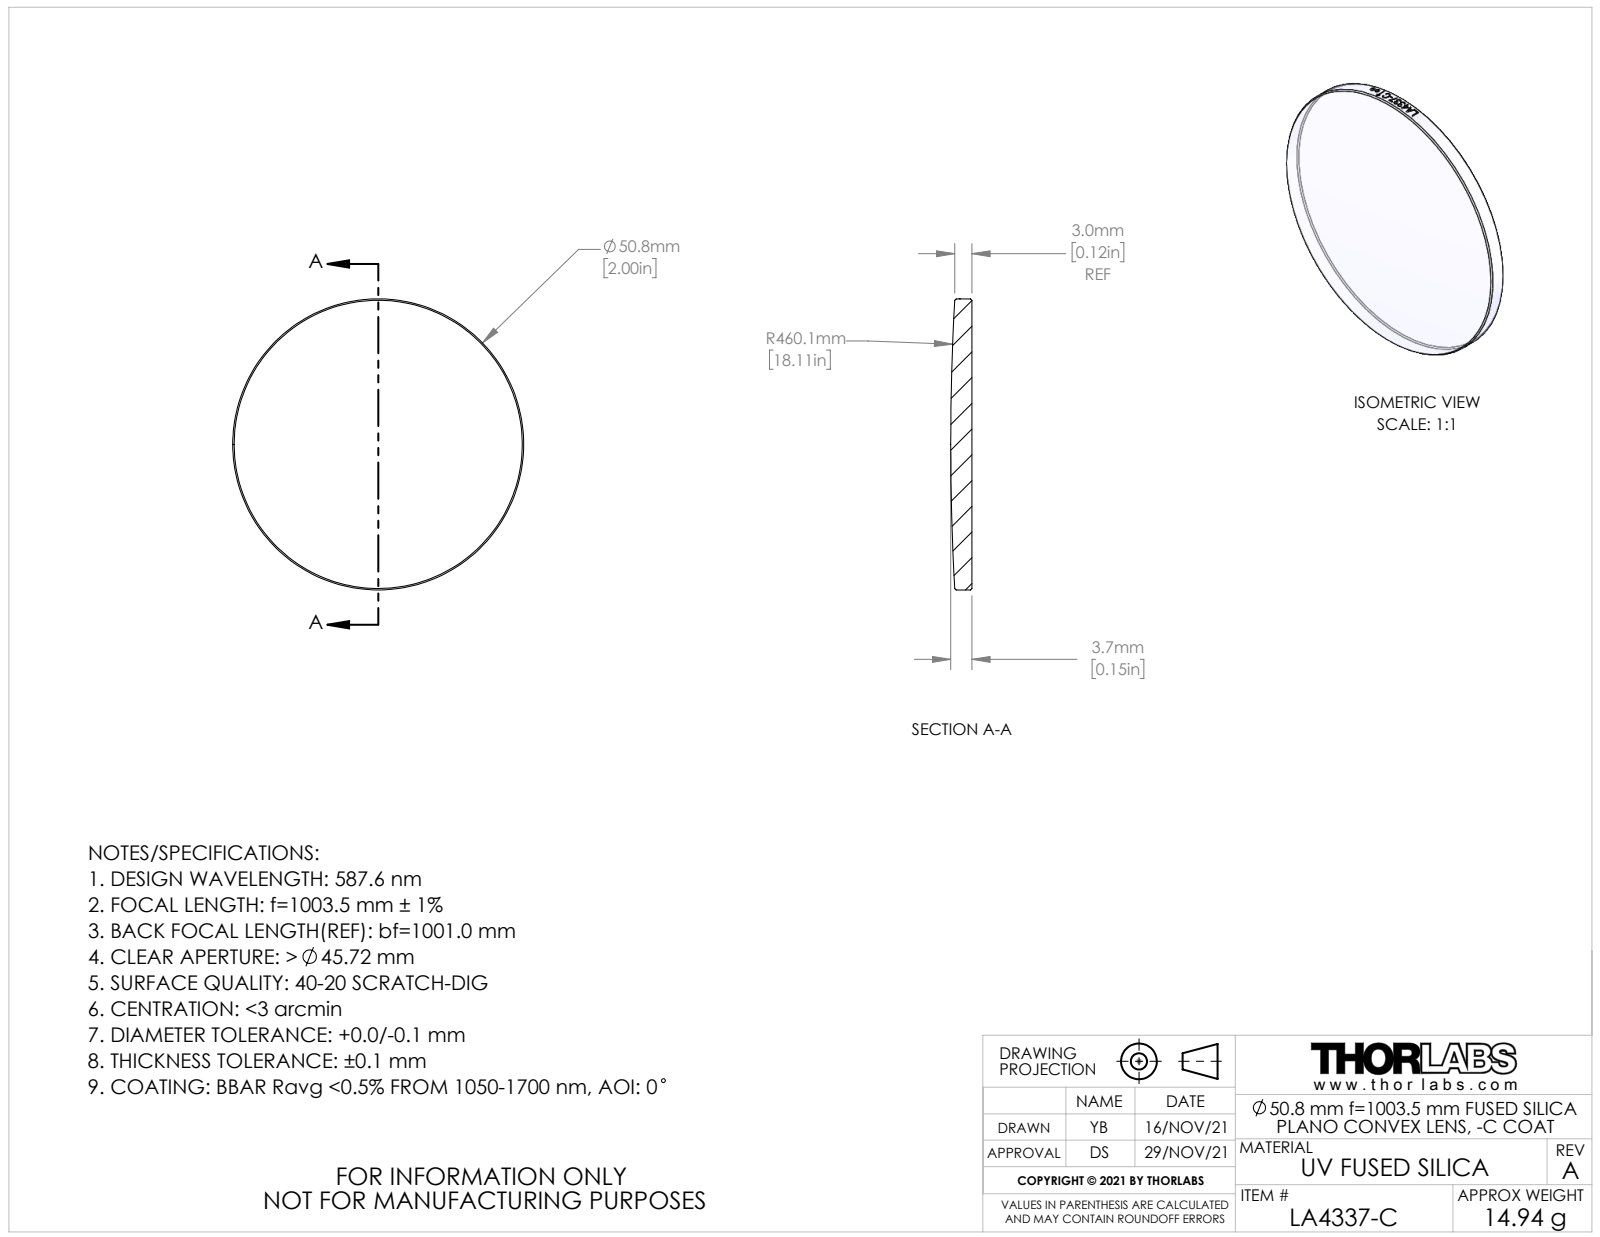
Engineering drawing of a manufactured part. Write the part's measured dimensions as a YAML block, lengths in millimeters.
part_name: "CTN018084-E0W; CTN018150"
step_written_by: "SolidWorks 2018 (AUTOMOTIVE_DESIGN)"
units: millimeters
bodies: {solids: 1, faces: 23, planar: 1, cylindrical: 16, other: 6}
overall_size: [50.8, 50.8, 3.7]
volume: 6781
surface_area: 4489
round_bosses_or_shafts:
  - {diameter: 50.8, count: 1}
